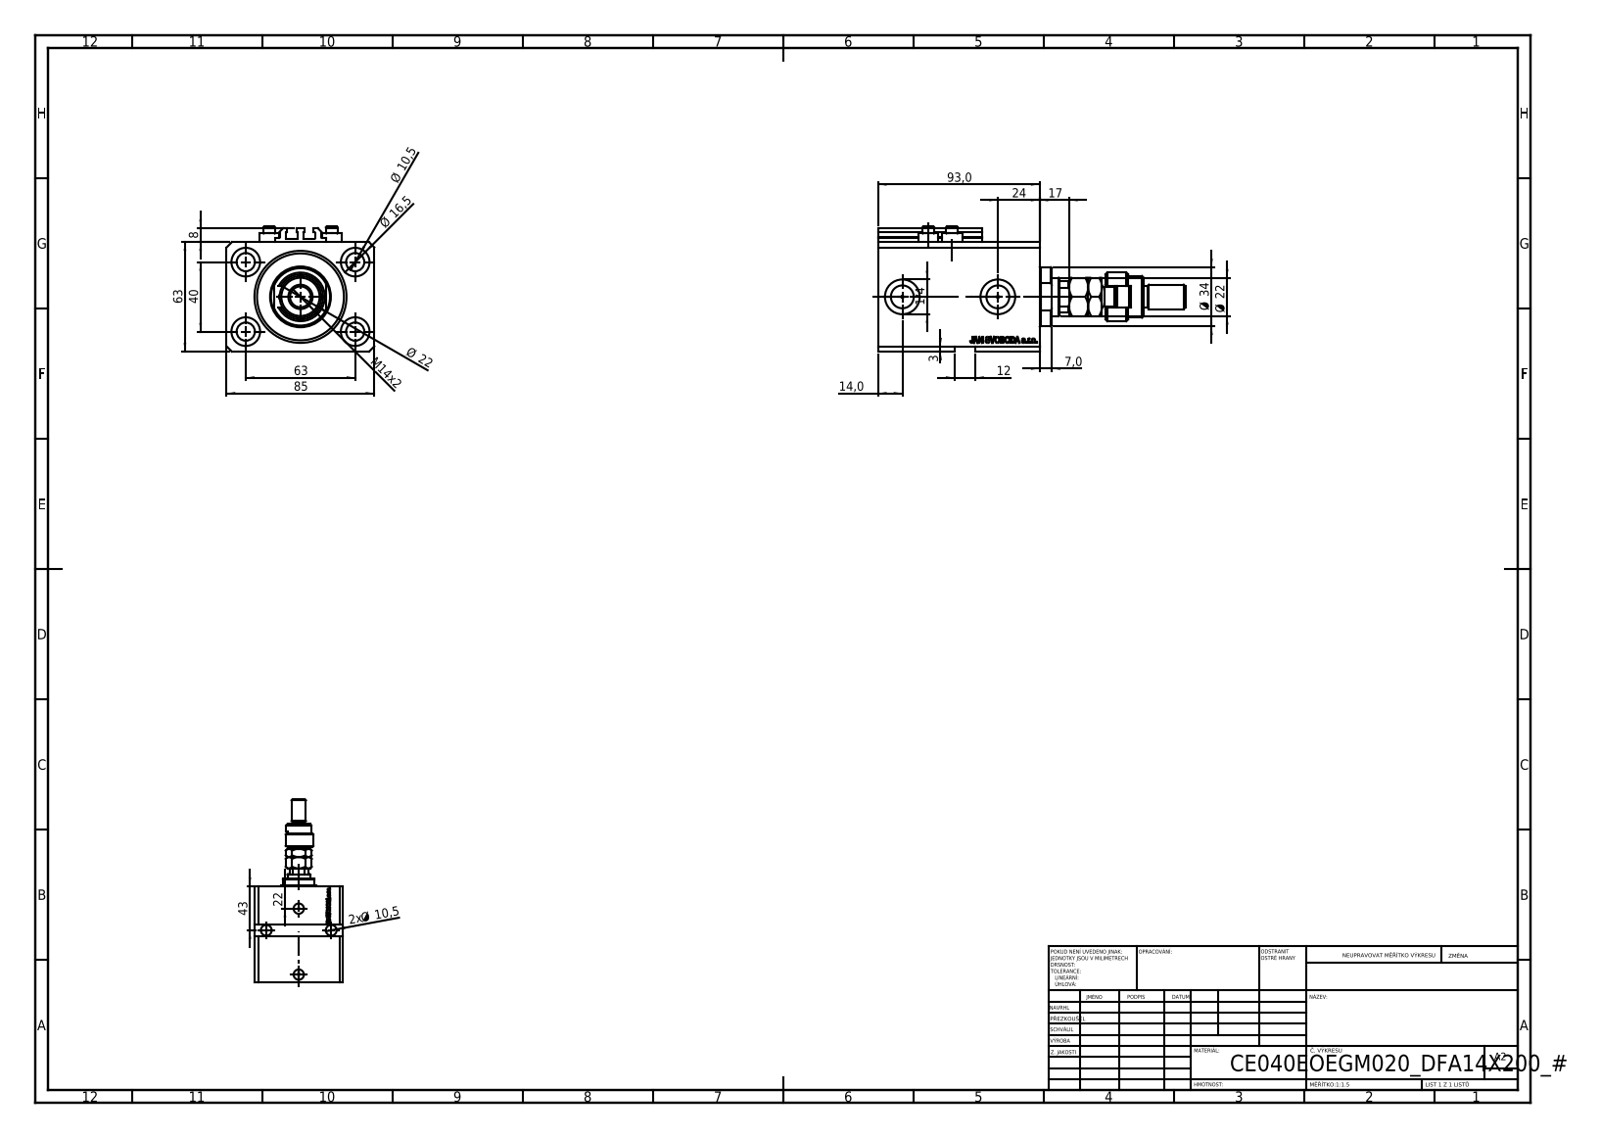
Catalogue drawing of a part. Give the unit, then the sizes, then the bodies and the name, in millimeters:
Units: millimetres
Overall size (bounding box): 177 × 85 × 72
Round holes (diameter × count): ⌀10.5 ×6, ⌀1.25 ×4, ⌀4 ×4, ⌀16.5 ×4, ⌀10 ×2, ⌀13.16 ×2, ⌀20 ×2, ⌀12.5 ×1, ⌀22 ×1, ⌀40 ×1, ⌀53 ×1
Round bosses / shafts (diameter × count): ⌀11.6 ×4, ⌀7 ×4, ⌀34 ×1, ⌀28 ×1, ⌀24 ×1, ⌀18 ×1, ⌀14 ×1, ⌀12 ×1
Partial cylindrical surfaces — rounded edges, fillets, slot ends (radius × count): R0.2 ×10, R9.75 ×1, R10.5 ×1
Main face-to-face distances: 63, 85, 93, 17, 76, 11.4, 64.6, 81.6, 3, 65
Hole centre spacings: 37.31, 63, 13.6, 15.4, 24.96, 28.02, 28.43, 33.62
Volume: 459 167 mm³ · Surface area: 103 748 mm²
Bodies: 10 solids, 1172 faces (563 planar, 139 cylindrical, 470 other)
Part name (STEP PRODUCT): V250CE_E_Body; ALLEN BOLT V250CE; FEMALE_PART_FOR_DFA; MFA (+2 more)
STEP written by: SolidWorks 2019 (CONFIG_CONTROL_DESIGN)
